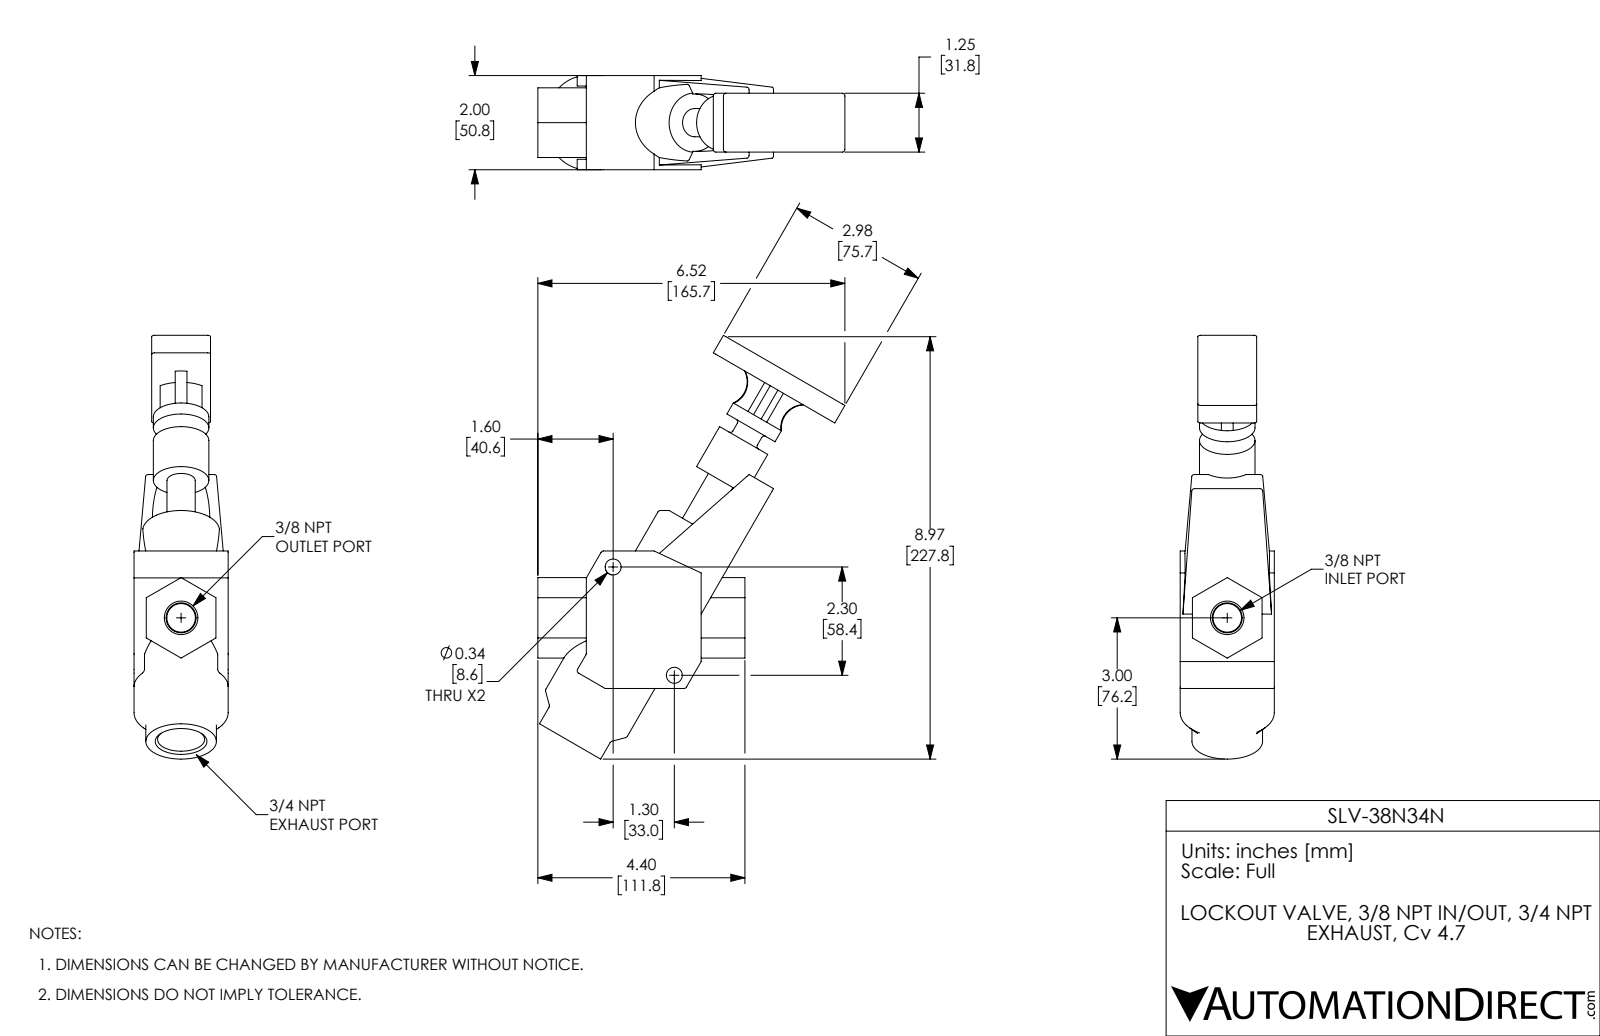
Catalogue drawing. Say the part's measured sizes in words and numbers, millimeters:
The part is named "SLV-38N34N; SLV-38N34N_HANDLE; SLV-38N34N_BODY". Its 3-D file was written by "SolidWorks 2017 (AUTOMOTIVE_DESIGN)". It is 2 solids with 131 faces: 57 planar, 40 cylindrical and 34 other. Overall it measures 228.6 by 165.7 by 50.8 millimeters. Its volume is 444 100 cubic millimeters and its surface area 70 710 square millimeters. Round holes: 2 of diameter 8.6, 1 of diameter 15.2, 1 of diameter 15.4. Round bosses or shafts: 1 of diameter 50.8, 1 of diameter 38.1, 1 of diameter 30, 1 of diameter 15.2. Partial cylindrical surfaces (rounded edges, fillets, slot ends): 10 of radius 1.5, 2 of radius 19.1, 1 of radius 15.5, 1 of radius 20.8. The main face-to-face distances are 50.8, 37.6, 10.9, 6.6, 44.2, 9.5, 41.3, 2.9, 34.7, 74.2. The hole center spacings are 67.1.
